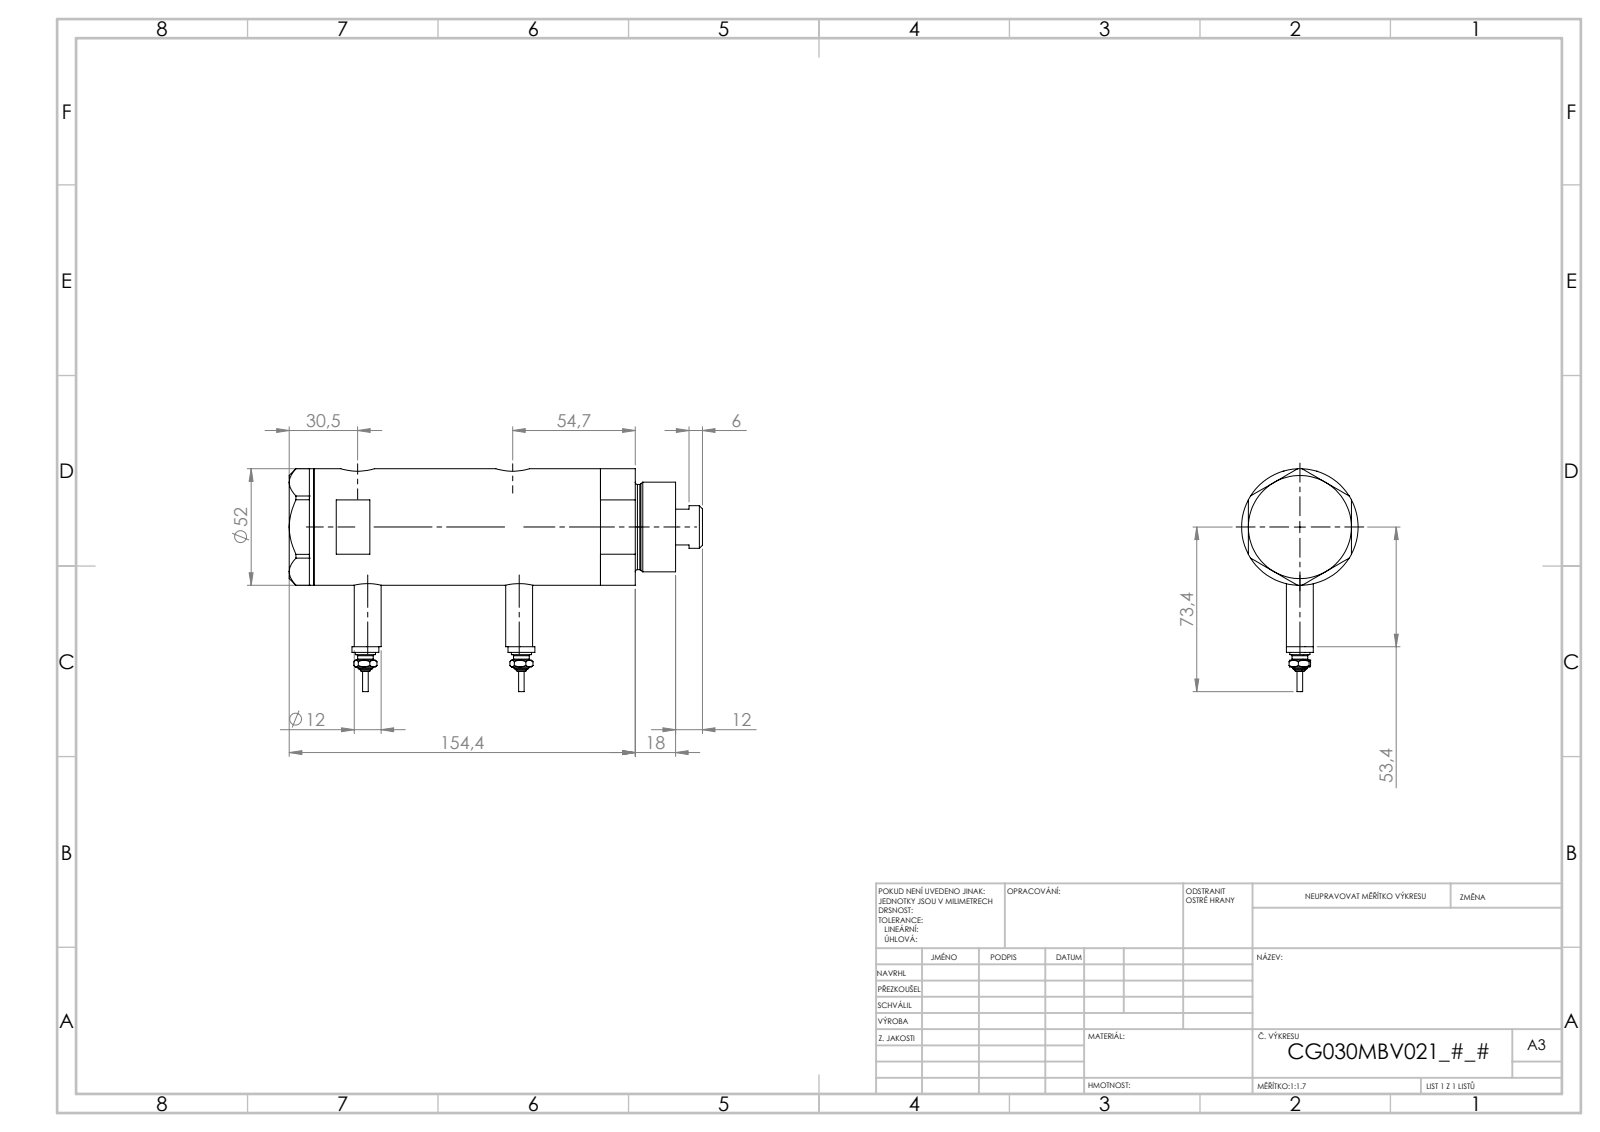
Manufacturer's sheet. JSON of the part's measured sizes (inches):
{"part_name": "V270CG_BACK; V270CG_MIDDLE; V270CG_VC; Switch (+1 more)", "step_written_by": "SolidWorks 2019 (CONFIG_CONTROL_DESIGN)", "units": "inches", "bodies": {"solids": 6, "faces": 226, "planar": 93, "cylindrical": 69, "other": 64}, "overall_size": [7.26, 3.913, 2.047], "volume_in3": 21.02, "surface_area_in2": 124.3, "round_holes": [[0.383, 2], [0.492, 2], [0.591, 2], [0.256, 1], [0.787, 1], [0.846, 1], [1.181, 1], [1.299, 1], [1.732, 1]], "round_bosses_or_shafts": [[0.472, 4], [0.354, 2], [0.276, 2], [0.177, 2], [0.098, 2], [2.047, 1], [1.575, 1], [1.496, 1]], "face_to_face_distances": [3.602, 0.937, 2.665, 0.433, 1.37, 4.035, 1.811, 1.433, 5.469, 5.035], "hole_center_spacings": [0.114, 0.177, 2.547, 2.661, 2.724, 2.839]}
